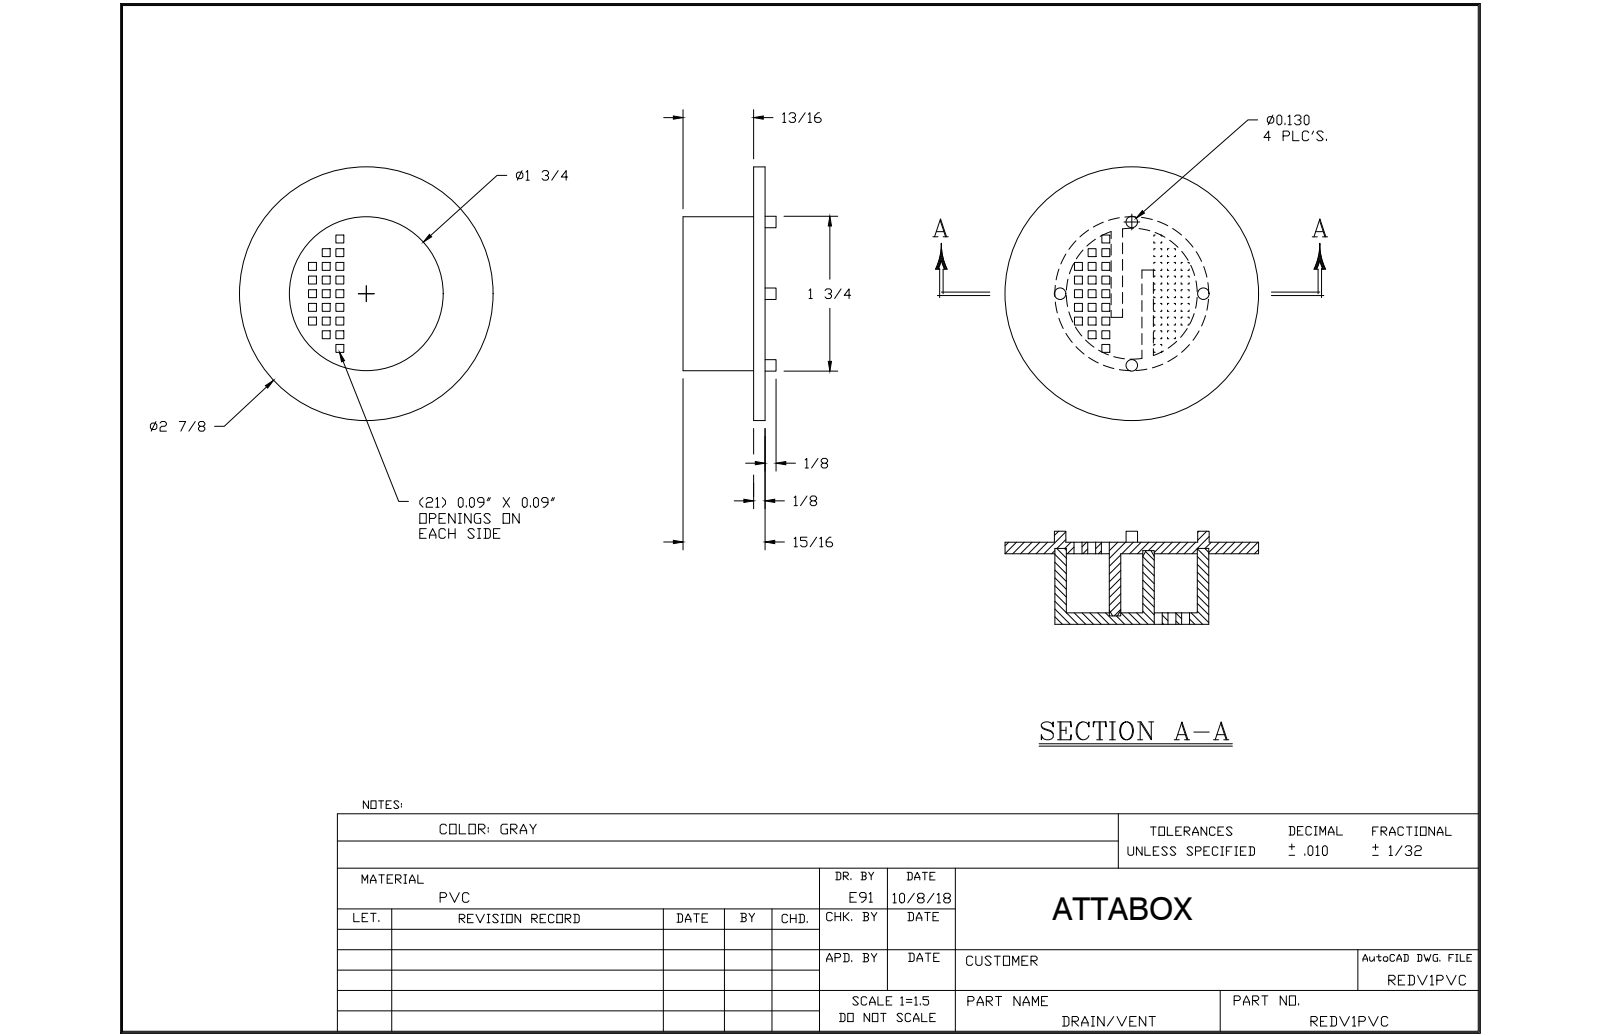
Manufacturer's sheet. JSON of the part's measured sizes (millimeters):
{"part_name": "REDV1PVC", "step_written_by": "SolidWorks 2017 (AUTOMOTIVE_DESIGN)", "units": "millimeters", "bodies": {"solids": 2, "faces": 199, "planar": 190, "cylindrical": 9, "other": 0}, "overall_size": [57.2, 57.2, 25.4], "volume_mm3": 21700, "surface_area_mm2": 16750, "round_holes": [[38.1, 1], [44.5, 1]], "round_bosses_or_shafts": [[3.2, 4], [57.2, 1]], "face_to_face_distances": [3.2, 19.1, 22.2, 15.9, 17.4, 1.6, 1.6, 3.2, 20.6, 0.8]}
